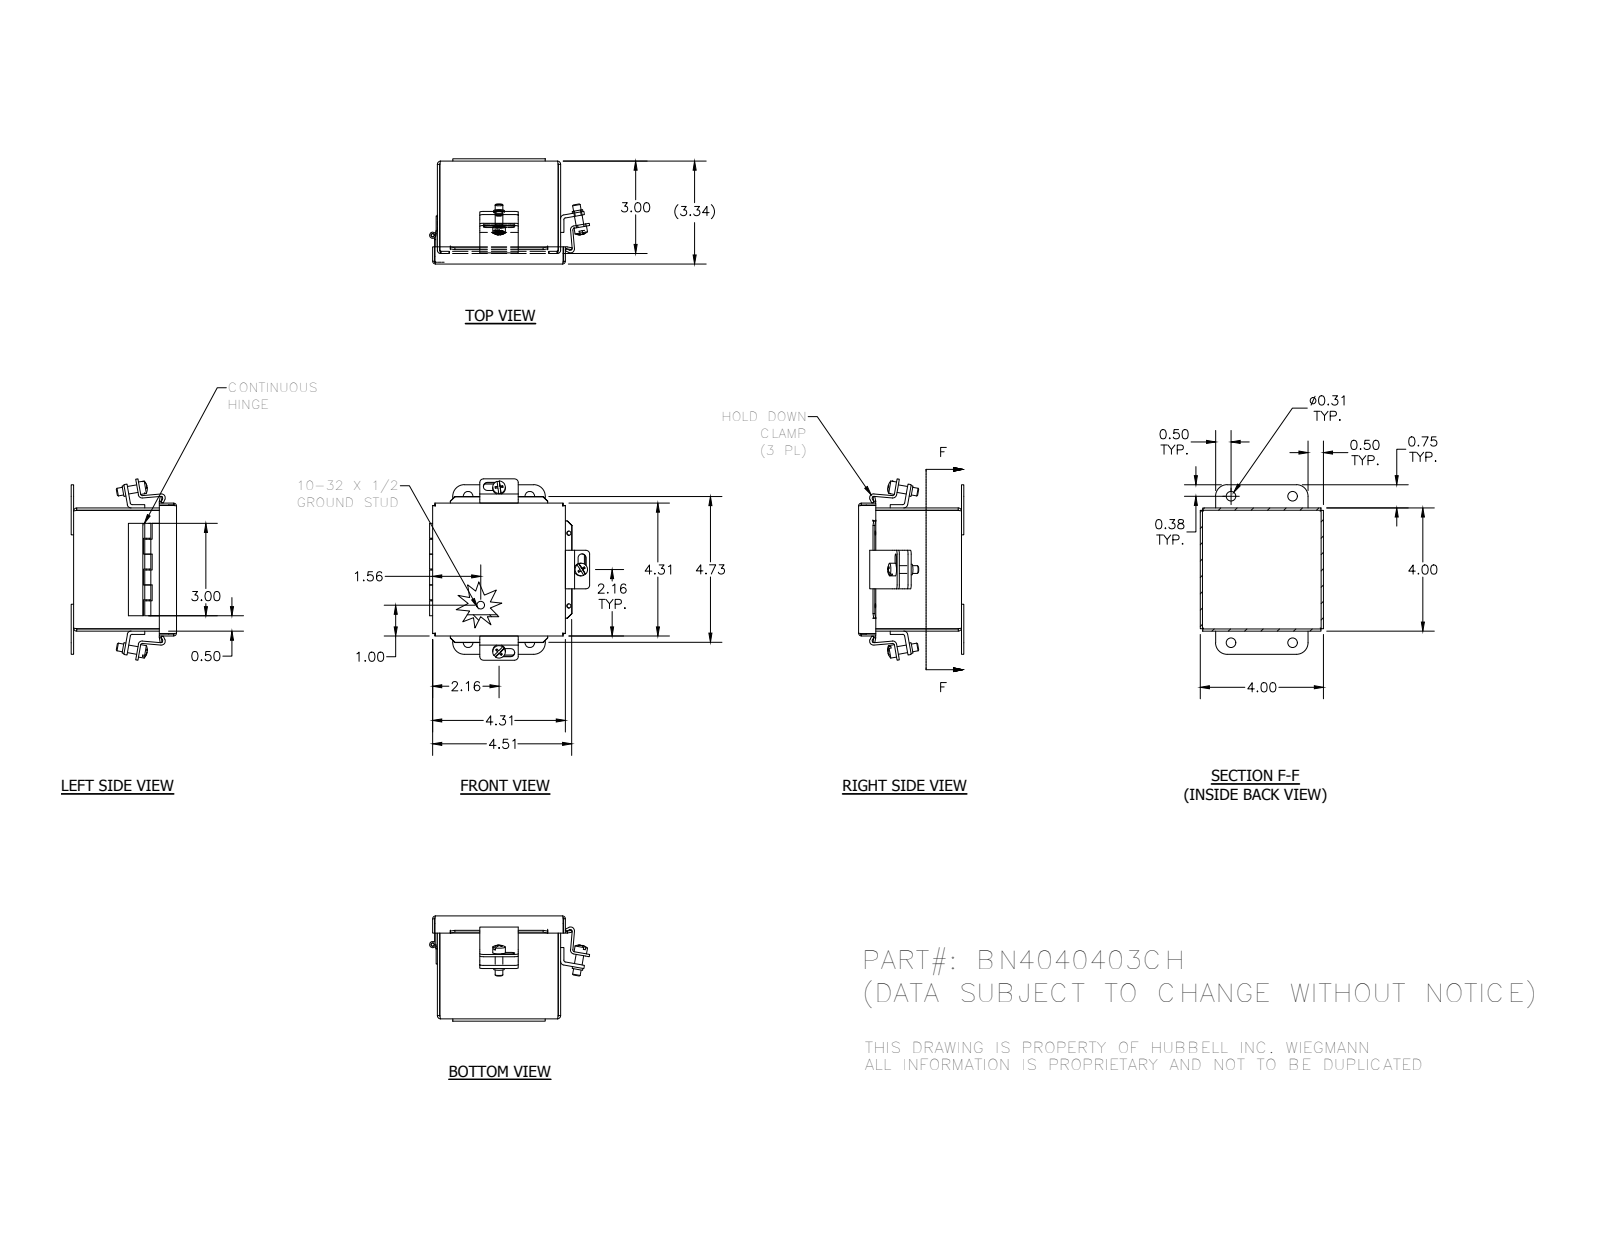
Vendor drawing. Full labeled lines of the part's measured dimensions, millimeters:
Part name (STEP PRODUCT): B_0404CH_LID; 316159; 38811; C1001 (+8 more)
STEP written by: Autodesk Inventor 2016 (AUTOMOTIVE_DESIGN)
Units: millimetres
Bodies: 13 solids, 338 faces (231 planar, 71 cylindrical, 36 other)
Overall size (bounding box): 139.7 × 129.18 × 82.78
Volume: 154 225 mm³ · Surface area: 164 664 mm²
Round holes (diameter × count): ⌀7.87 ×4, ⌀3.56 ×2, ⌀2.96 ×1, ⌀4.98 ×1
Round bosses / shafts (diameter × count): ⌀6.35 ×2, ⌀10.4 ×1, ⌀8.74 ×1, ⌀5.08 ×1, ⌀4.83 ×1, ⌀2.54 ×1
Partial cylindrical surfaces — rounded edges, fillets, slot ends (radius × count): R1.19 ×8, R3.07 ×8, R1.98 ×4, R3.17 ×4, R3.48 ×4, R9.53 ×4, R0.79 ×3, R1.6 ×3
Main face-to-face distances: 1.88, 99.72, 79.38, 1.5, 101.6, 97.84, 80.88, 77.5, 79, 1.9
Hole centre spacings: 50.8, 120.65, 130.91, 61.08
